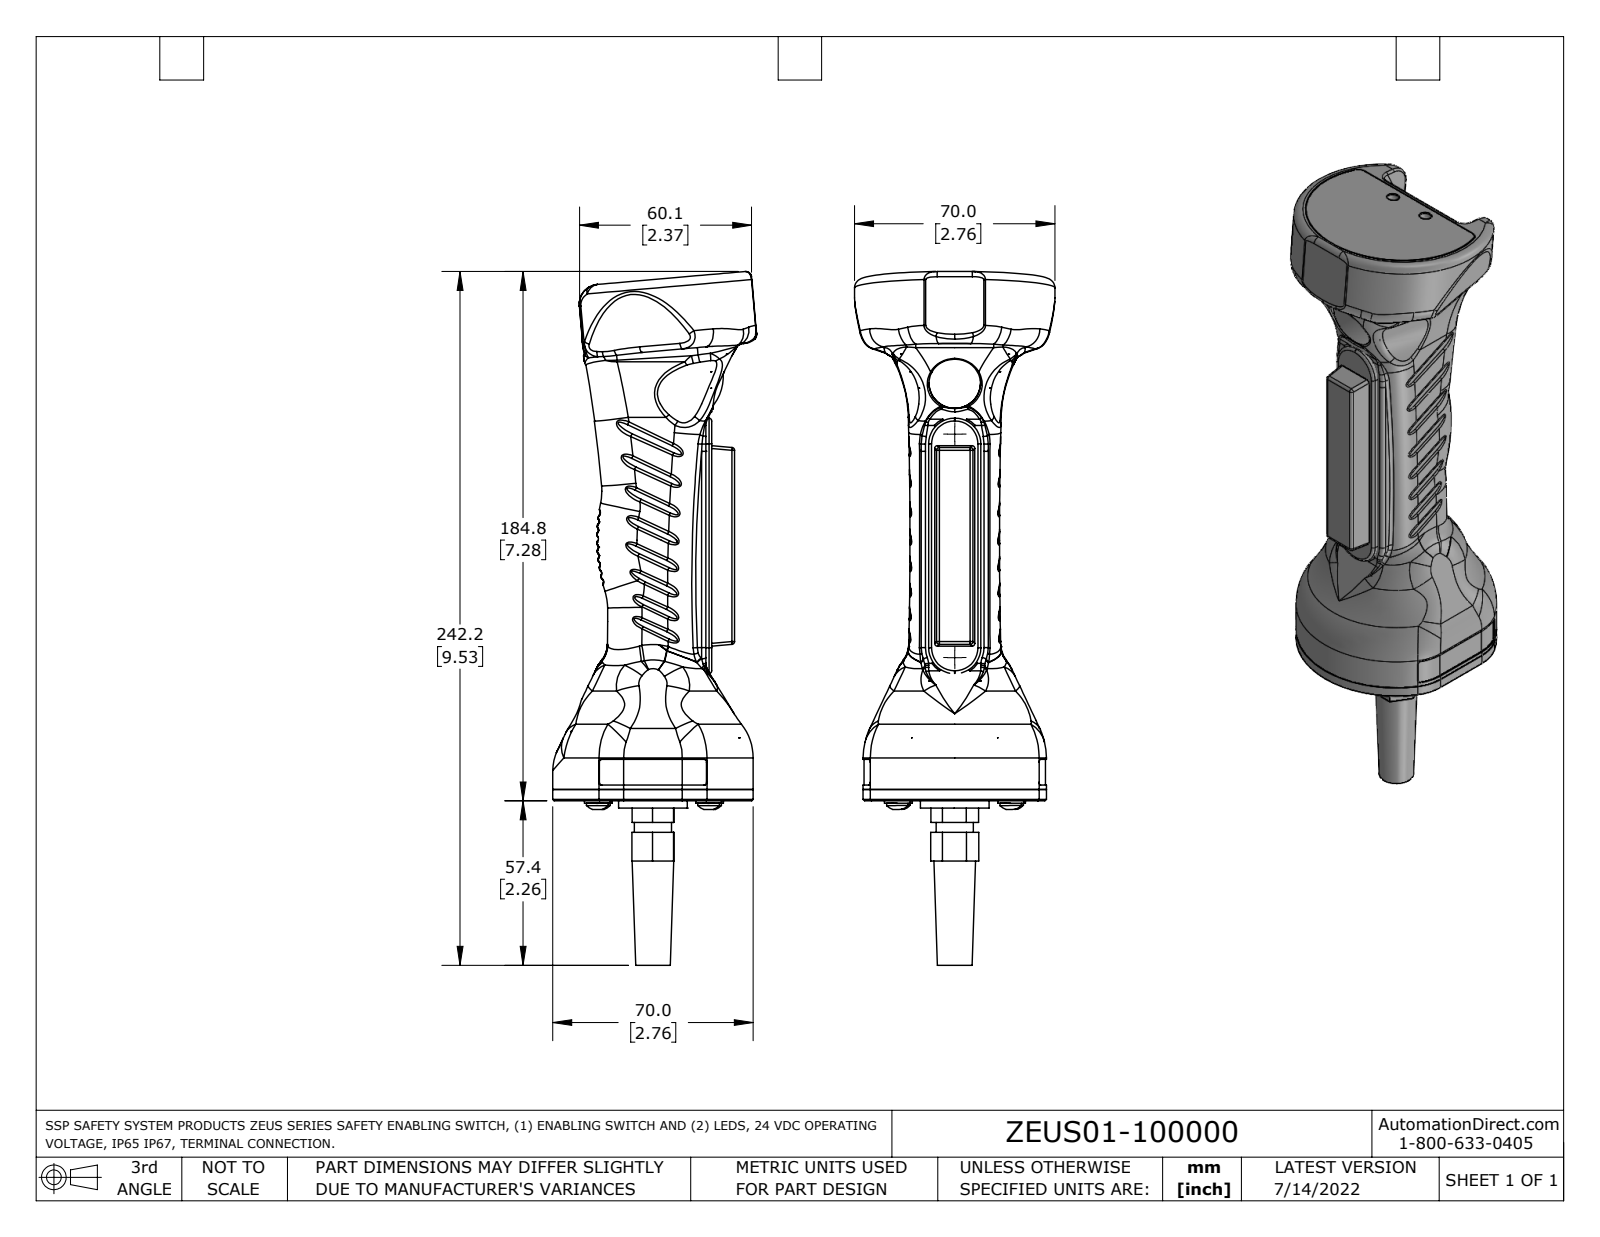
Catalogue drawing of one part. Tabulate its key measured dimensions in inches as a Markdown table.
| quantity | value |
| --- | --- |
| part name | ZEUS01-100000 |
| STEP written by | SolidWorks 2021 (AUTOMOTIVE_DESIGN) |
| units | inches |
| bodies | 16 solids, 1129 faces (318 planar, 396 cylindrical, 415 other) |
| overall size | 9.535 × 2.803 × 2.756 |
| volume | 23.26 in³ |
| surface area | 117.8 in² |
| round holes (diameter × count) | 0.132 × 4, 0.169 × 4, 0.177 × 4, 0.197 × 4, 0.098 × 2, 0.11 × 2, 0.165 × 2, 0.173 × 2, 0.331 × 2, 0.551 × 1, 0.709 × 1, 0.728 × 1 |
| round bosses / shafts (diameter × count) | 0.354 × 4, 0.295 × 4, 0.157 × 4, 0.039 × 4, 0.236 × 2, 0.945 × 1, 0.827 × 1, 0.776 × 1 |
| partial cylindrical surfaces (radius × count) | 0.005 × 96, 0.039 × 51, 0.028 × 48, 0.079 × 21, 0.118 × 10, 0.031 × 7, 0.012 × 5, 0.618 × 4 |
| main face-to-face distances | 0.157, 0.079, 0.02, 0.014, 0.065, 0.059, 0.098, 0.177, 0.571, 0.256 |
| hole center spacings | 1.531, 0.404, 0.63, 0.867, 1.181, 1.558, 2.184, 0.513 |
